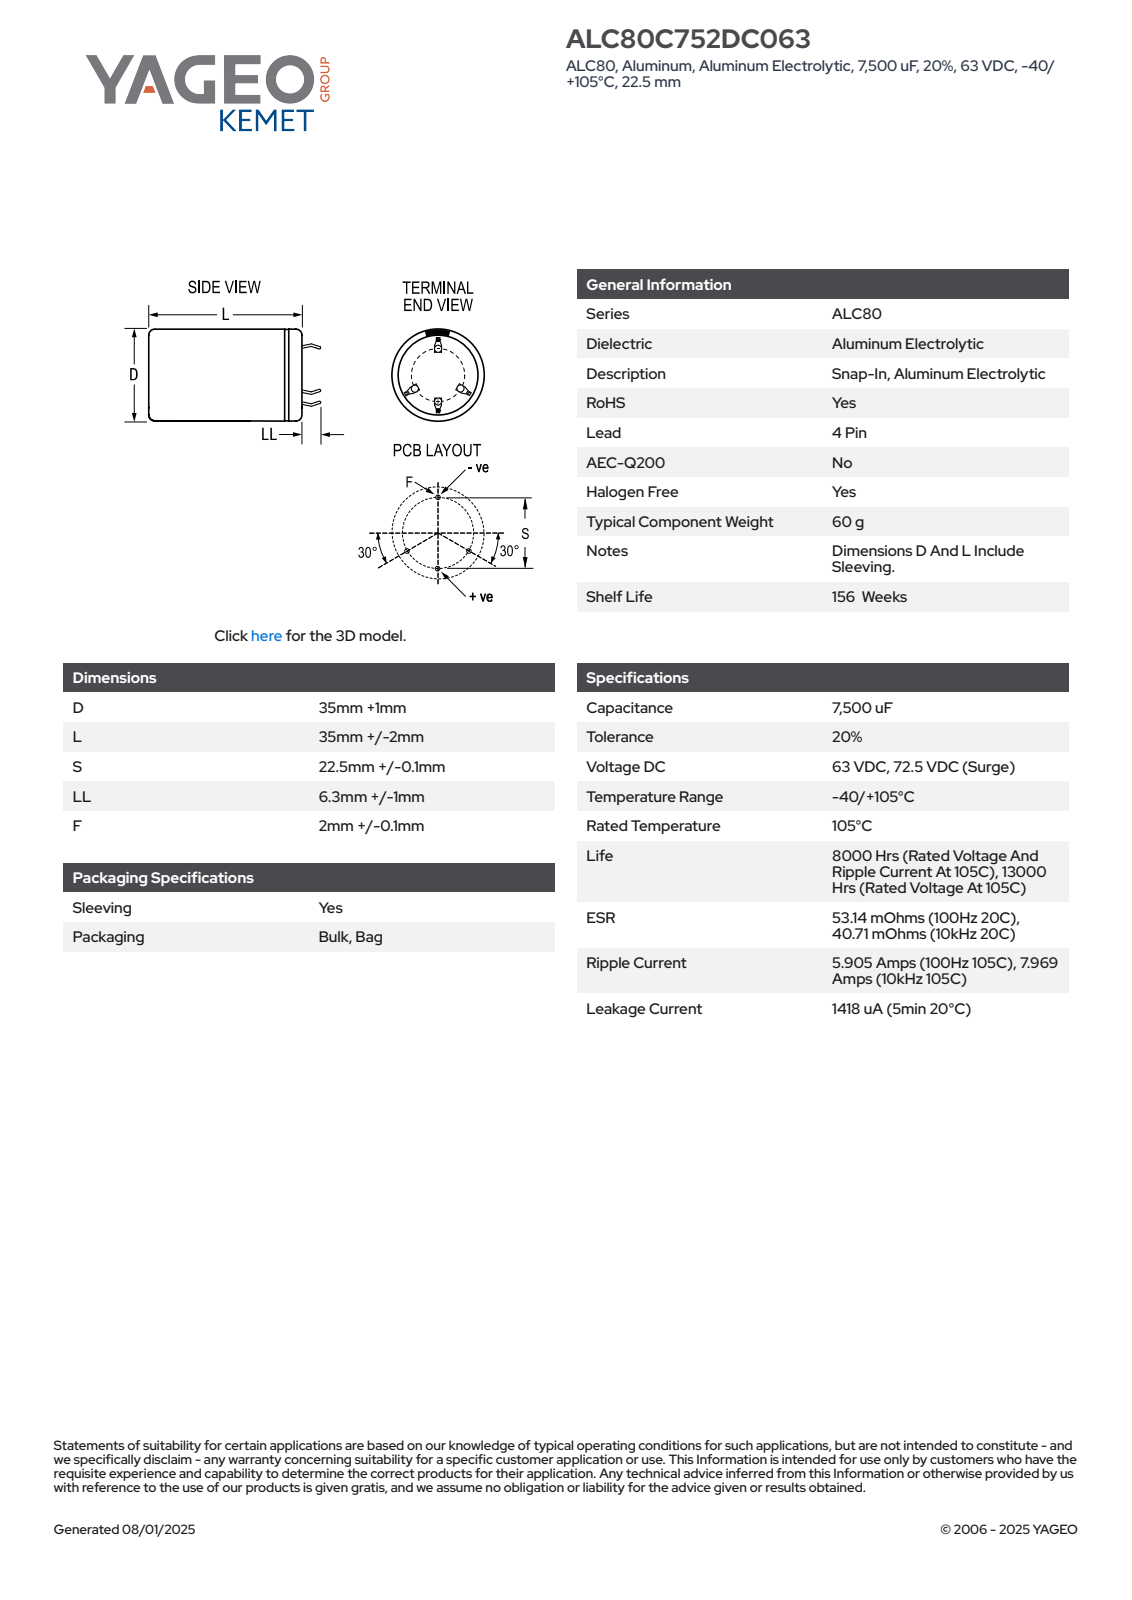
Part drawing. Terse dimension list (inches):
name: CARS_K4P_35X35_D36L37S22.5LL7.3F2.1
written by: SolidWorks 2014 (AUTOMOTIVE_DESIGN)
unit: in
bodies: 1 solid, 134 faces (80 planar, 15 cylindrical, 39 other)
size: 1.744 × 1.417 × 1.417
volume: 2.267 in³; area: 9.711 in²
holes: 1× ⌀1.254
bosses: 1× ⌀1.417
rounds: 1× R0.708
face distances: 1.456, 1.476, 0.02, 0.024, 0.022, 0.03, 0.053, 0.926, 0.083, 0.903
